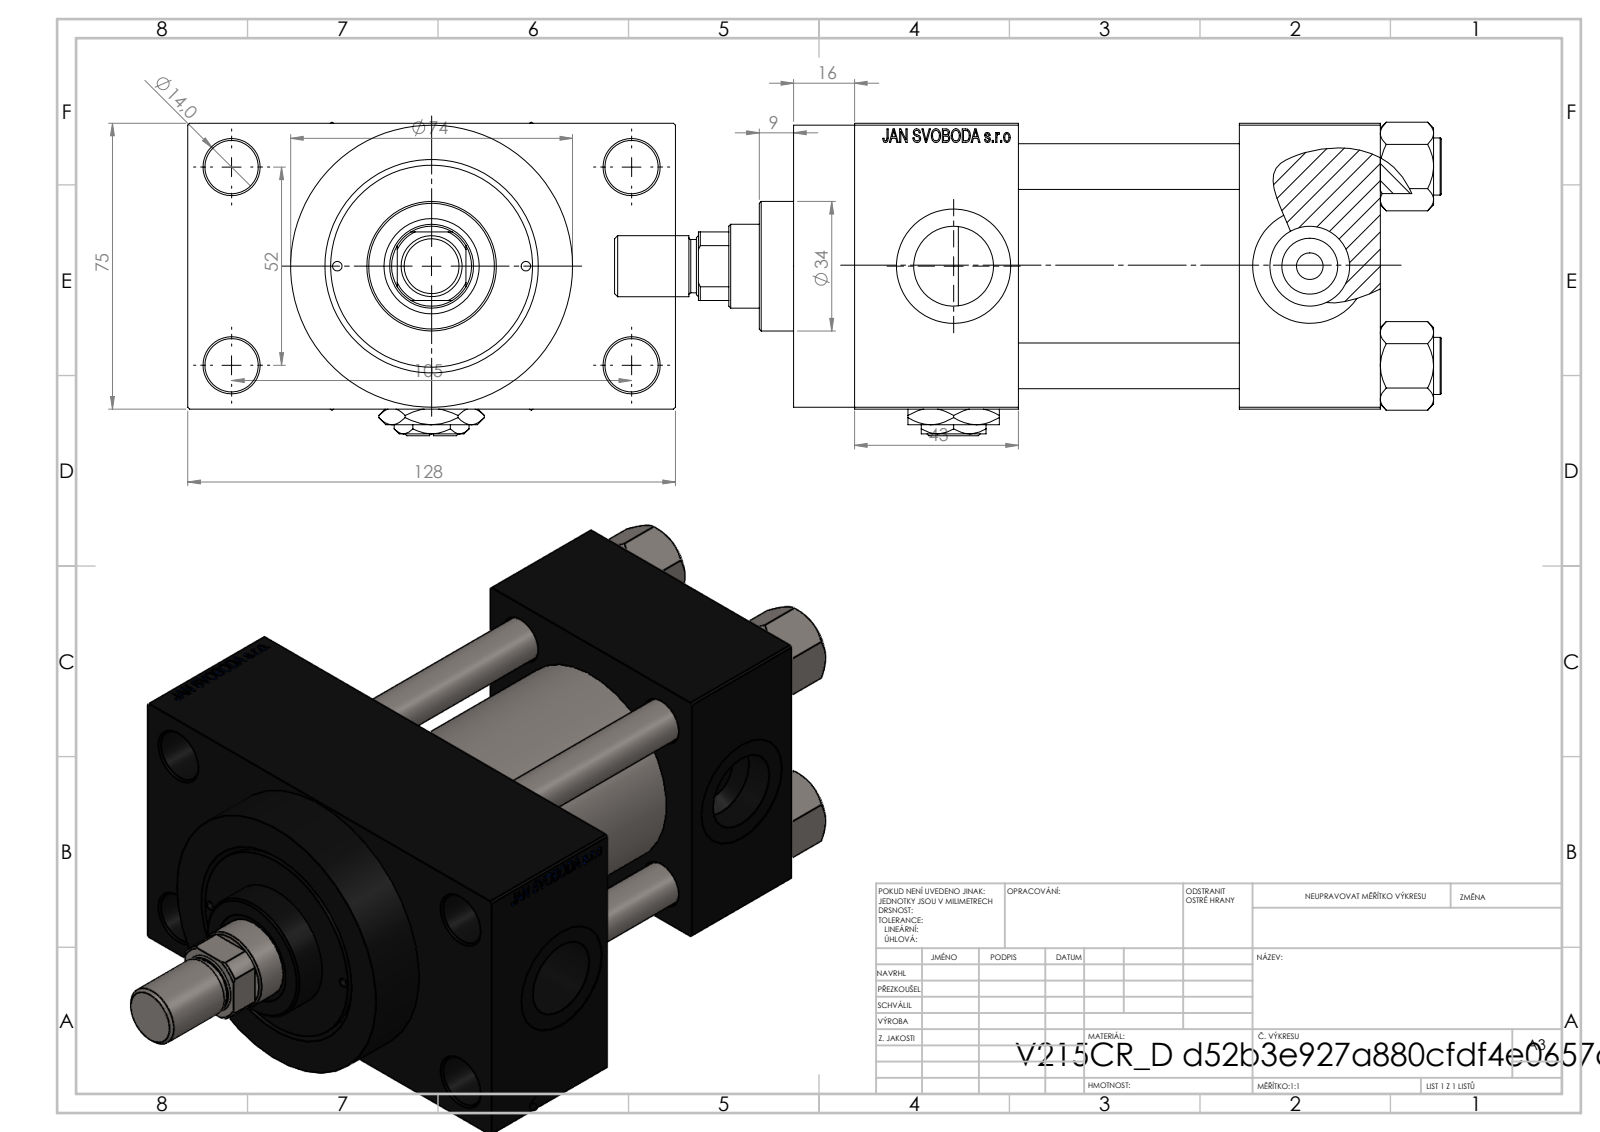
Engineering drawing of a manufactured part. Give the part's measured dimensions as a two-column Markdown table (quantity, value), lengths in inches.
| quantity | value |
| --- | --- |
| part name | V215CR_D_TYCINKA; NUT_M5_D; ROD_END_AH; V215CR_VCP_D (+3 more) |
| STEP written by | SolidWorks 2019 (CONFIG_CONTROL_DESIGN) |
| units | inches |
| bodies | 13 solids, 1173 faces (527 planar, 100 cylindrical, 546 other) |
| overall size | 8.543 × 5.039 × 3.239 |
| volume | 48.8 in³ |
| surface area | 263 in² |
| round holes (diameter × count) | 0.472 × 4, 0.551 × 4, 0.825 × 3, 1.181 × 3, 0.098 × 2, 0.276 × 2, 0.413 × 1, 0.866 × 1, 0.984 × 1, 1.614 × 1, 1.969 × 1, 2.087 × 1 |
| round bosses / shafts (diameter × count) | 0.591 × 4, 2.913 × 1, 2.205 × 1, 1.339 × 1, 0.63 × 1, 0.551 × 1 |
| partial cylindrical surfaces (radius × count) | 0.413 × 1 |
| main face-to-face distances | 2.953, 2.283, 1.457, 3.74, 1.043, 3.976, 5.433, 1.693, 3.996, 0.63 |
| hole center spacings | 1.031, 1.037, 1.456, 1.497, 2.059, 2.253, 2.3, 2.307 |
